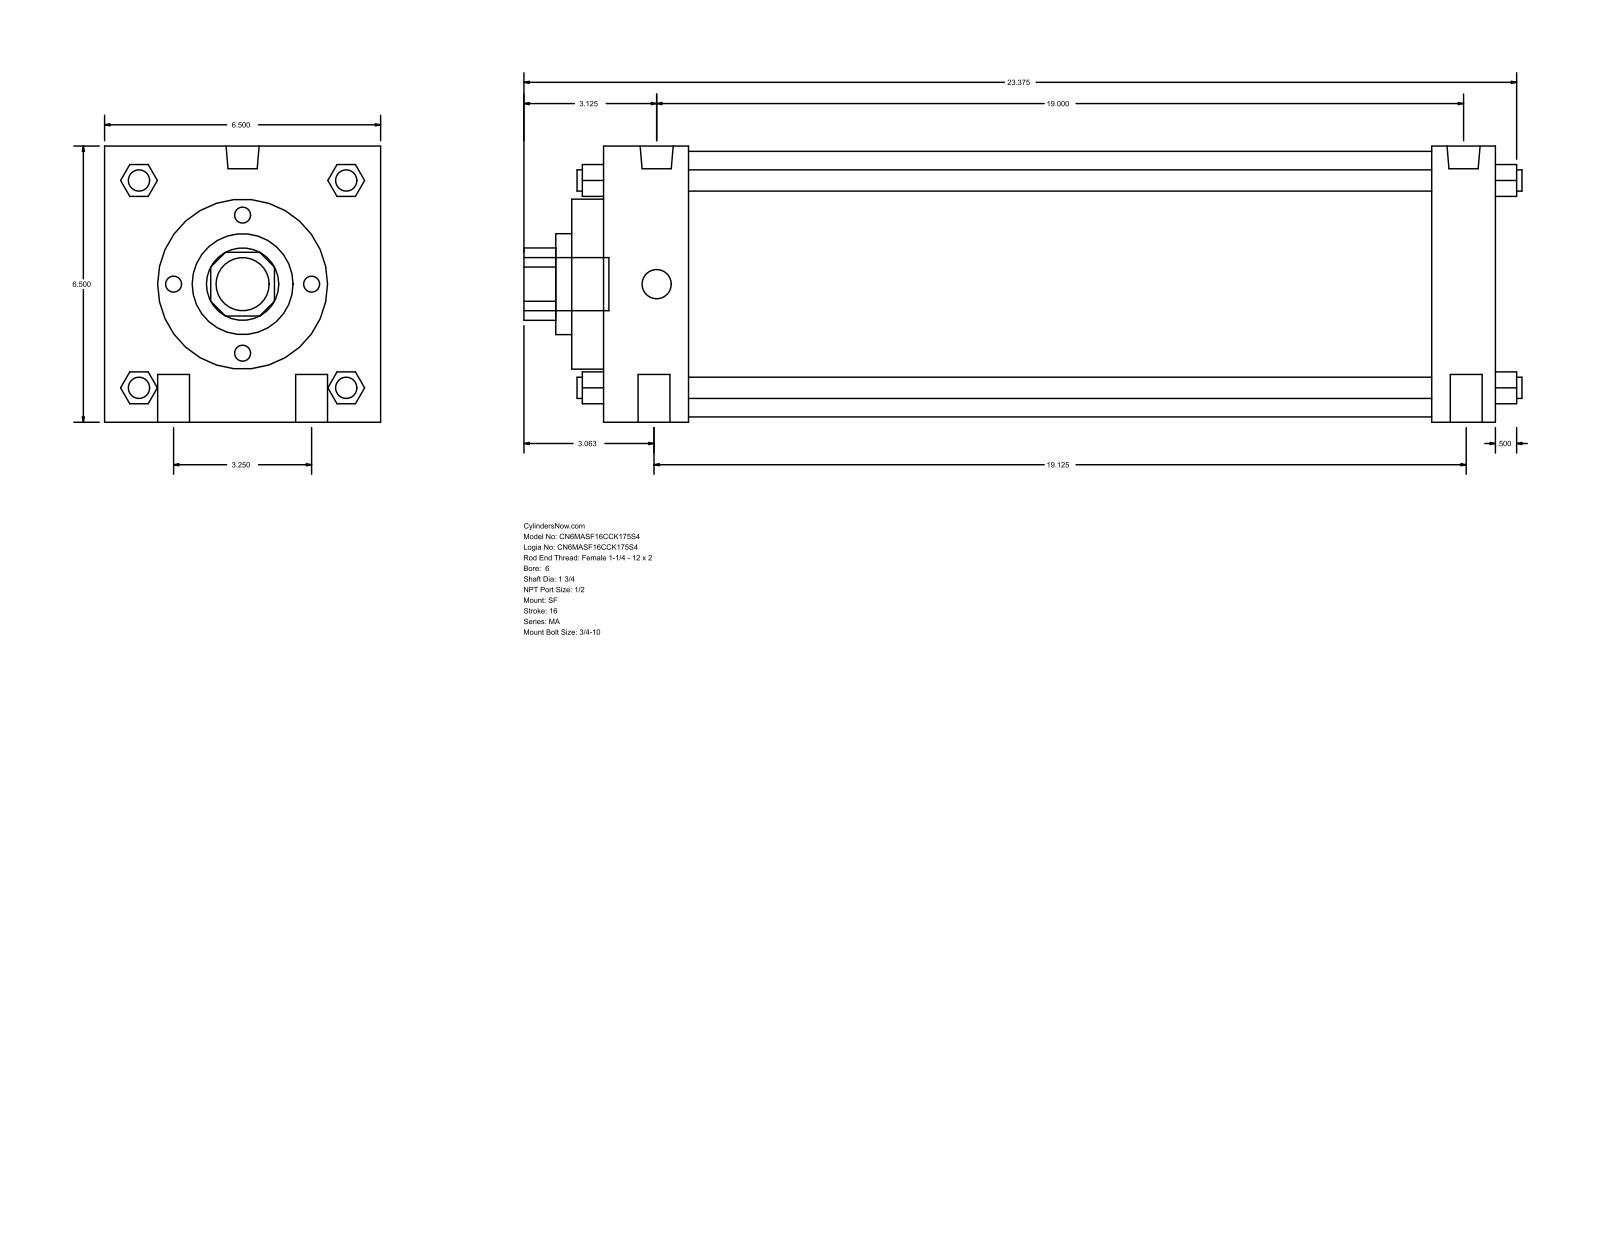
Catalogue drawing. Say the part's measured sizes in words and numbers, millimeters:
The part is named "MA_SF__0600_1.75". Its 3-D file was written by "GSSL Pune (CONFIG_CONTROL_DESIGN)". It is 0 solids with 126 faces: 95 planar, 31 cylindrical and 0 other. Overall it measures 596.9 by 165.1 by 165.1 millimeters. Round holes: 1 of diameter 44.45, 1 of diameter 60.33, 1 of diameter 101.6, 1 of diameter 158.75. Round bosses or shafts: 4 of diameter 19.05, 4 of diameter 12.7, 2 of diameter 19.77, 2 of diameter 17.46, 1 of diameter 31.75. Partial cylindrical surfaces (rounded edges, fillets, slot ends): 1 of radius 21.63. The main face-to-face distances are 165.1, 533.4, 19.05, 50.8, 38.1, 495.3, 444.5, 482.6, 69.85, 514.35.
